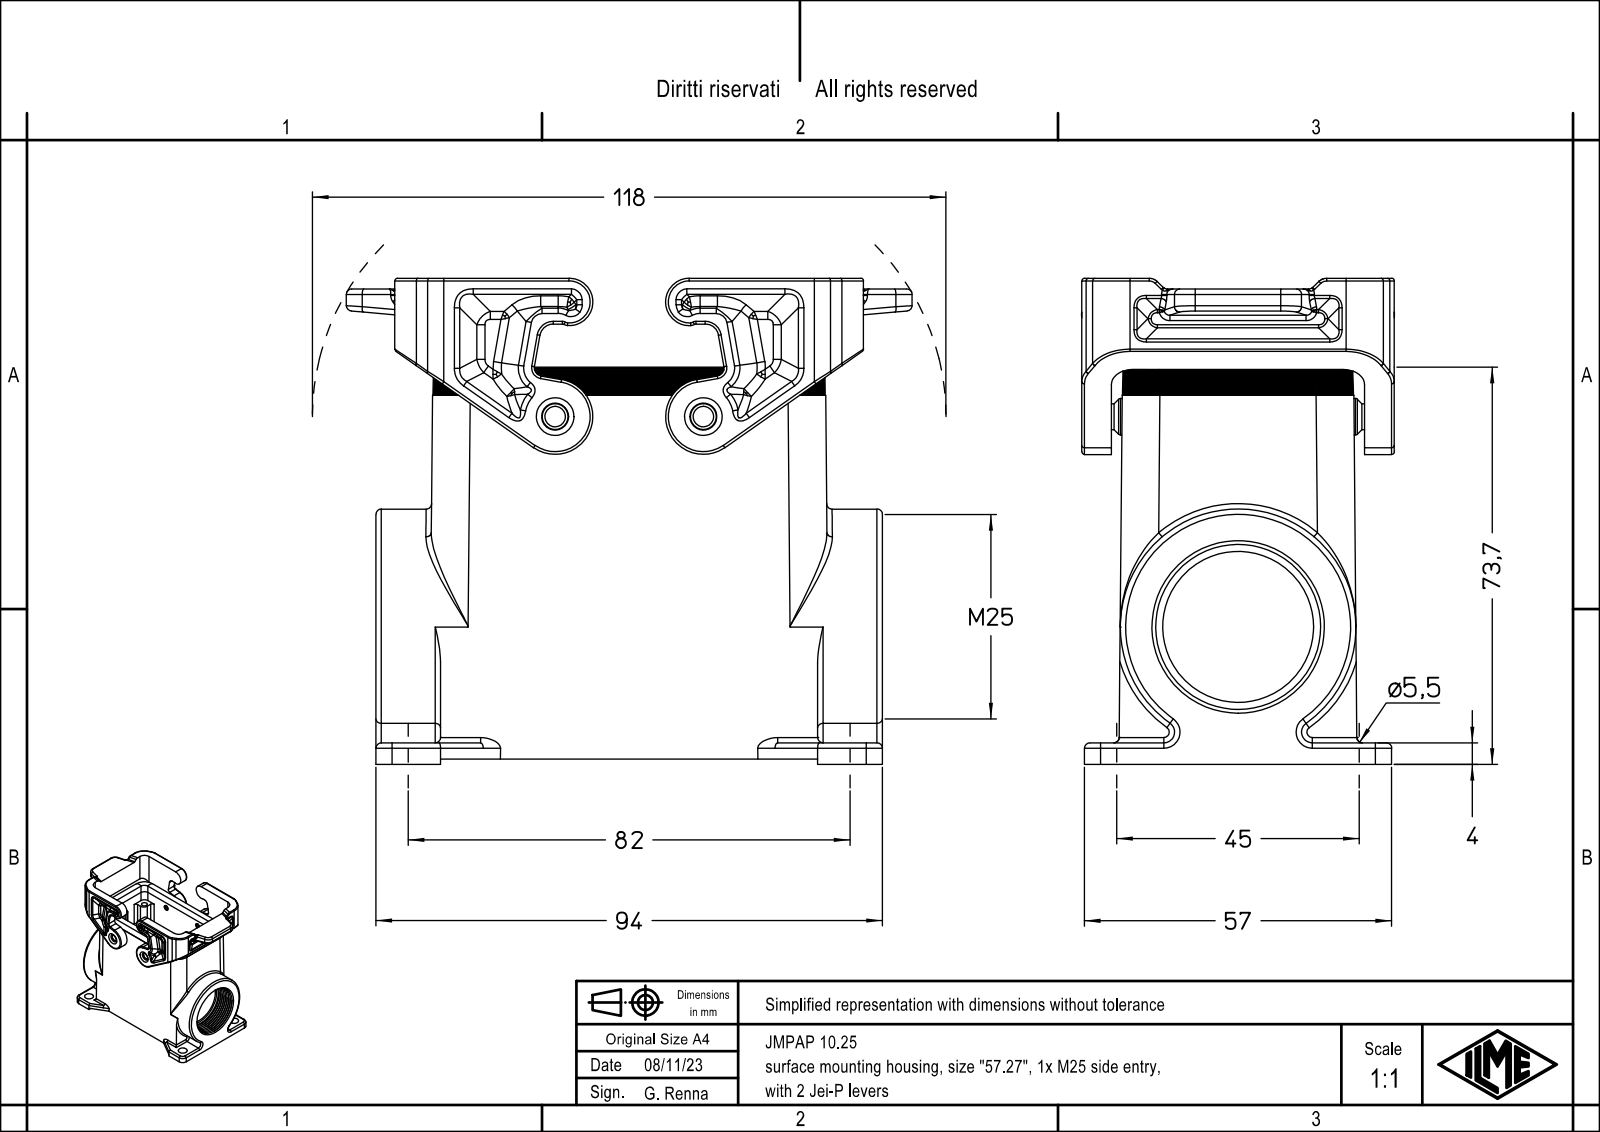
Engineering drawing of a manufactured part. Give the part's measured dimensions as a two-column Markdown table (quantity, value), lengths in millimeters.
| quantity | value |
| --- | --- |
| part name | JMPAP 10.25 |
| STEP written by | Creo Elements/Direct Modeling 20.1B 02-Apr-2019 (C) Parametric Technology GmbH (AUTOMOTIVE_DESIGN) |
| units | millimeters |
| bodies | 1 solid, 862 faces (171 planar, 310 cylindrical, 381 other) |
| overall size | 105 × 90.2 × 58.08 |
| volume | 139 802 mm³ |
| surface area | 55 882 mm² |
| round holes (diameter × count) | 3 × 4, 3.5 × 4, 5.5 × 4, 4.8 × 2, 23.6 × 1 |
| round bosses / shafts (diameter × count) | 6.8 × 2, 43.75 × 1 |
| partial cylindrical surfaces (radius × count) | 0.5 × 50, 1 × 44, 3 × 38, 2 × 26, 1.5 × 12, 4 × 12, 6 × 12, 7 × 10 |
| main face-to-face distances | 3, 8.5, 1, 4, 47, 85.5, 94, 5.5, 52.5, 7 |
| hole center spacings | 15.4, 38.11, 70.08, 78.27, 27, 45, 57, 63.07 |
